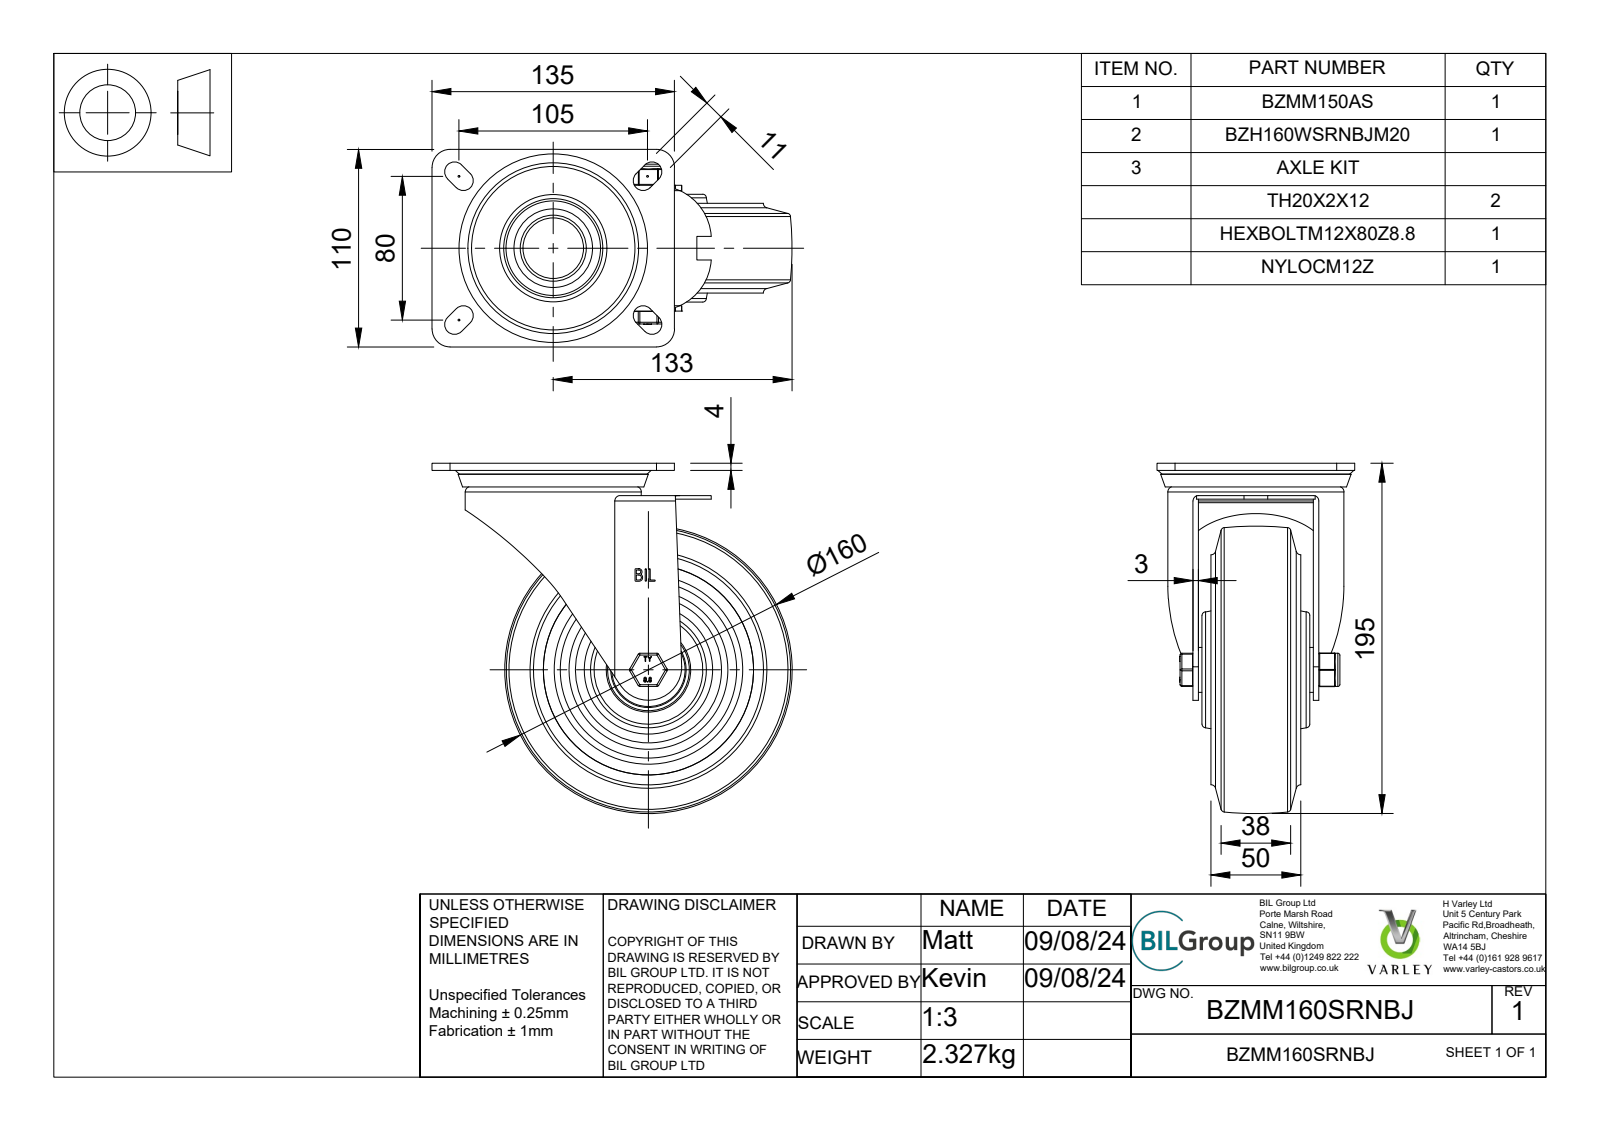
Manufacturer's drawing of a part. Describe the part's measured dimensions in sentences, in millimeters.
The part is named "BZMM160SRNBJ v3; BZMM150AS - 2 - 64 v2; ZINC PLATED, PRESSED STEEL TOP PLATE; ZINC PLATED, PRESSED STEEL TOP PLATE Geometry (+7 more)". Its 3-D file was written by "Autodesk Translation Framework v13.14.0.145 (AUTOMOTIVE_DESIGN)". It is 77 solids with 1115 faces: 420 planar, 198 cylindrical and 497 other. Overall it measures 200.5 by 195 by 110 millimeters. Its volume is 934 377 cubic millimeters and its surface area 275 065 square millimeters. Round holes: 1 of diameter 12, 1 of diameter 12.2, 1 of diameter 14, 1 of diameter 20, 1 of diameter 28.5, 1 of diameter 30.8, 1 of diameter 33.75, 1 of diameter 39.75, 1 of diameter 40, 1 of diameter 40.3, 1 of diameter 40.5, 1 of diameter 42. Round bosses or shafts: 1 of diameter 98, 1 of diameter 78, 1 of diameter 50, 1 of diameter 40.8, 1 of diameter 31.3, 1 of diameter 27, 1 of diameter 25, 1 of diameter 24. Partial cylindrical surfaces (rounded edges, fillets, slot ends): 18 of radius 0.5, 12 of radius 1, 8 of radius 5.5, 4 of radius 10, 2 of radius 1.5, 2 of radius 3, 2 of radius 29.97, 1 of radius 16.5. The main face-to-face distances are 5, 9, 7, 3, 4, 2, 16, 60, 10, 57.
